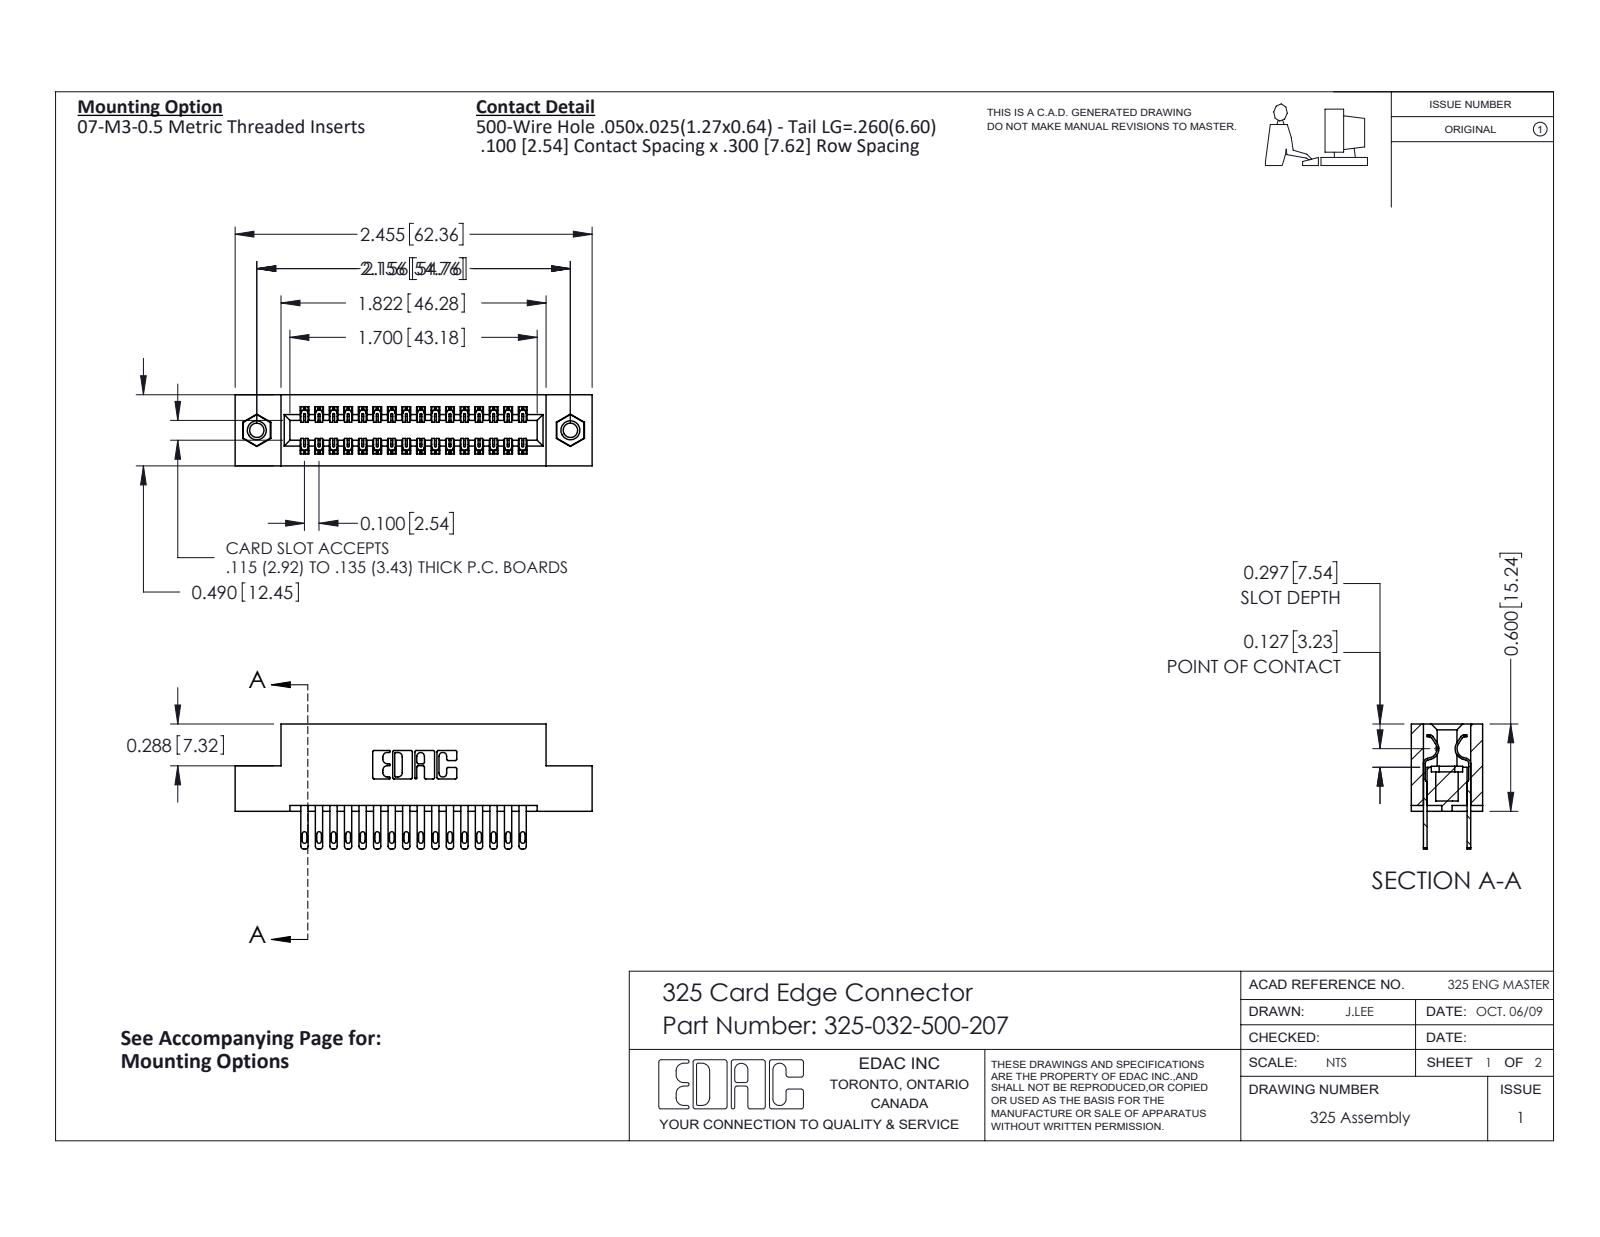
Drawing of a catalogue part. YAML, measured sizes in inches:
part_name: "345-250-001_345-250-005-103; 325-292-001_325-293-100; 325 Part_TI; 325-032-500-207"
step_written_by: "SolidWorks 2016 (CONFIG_CONTROL_DESIGN)"
units: inches
bodies: {solids: 35, faces: 1710, planar: 1062, cylindrical: 632, other: 16}
overall_size: [2.455, 0.86, 0.49]
volume: 0.482
surface_area: 14.43
round_holes:
  - {diameter: 0.098, count: 2}
  - {diameter: 0.125, count: 2}
  - {diameter: 0.16, count: 2}
round_bosses_or_shafts:
  - {diameter: 0.155, count: 2}
partial_cylinders:
  - {radius: 0.006, count: 48}
  - {radius: 0.016, count: 32}
  - {radius: 0.02, count: 32}
  - {radius: 0.01, count: 22}
  - {radius: 0.007, count: 6}
  - {radius: 0.031, count: 6}
  - {radius: 0.026, count: 3}
  - {radius: 0.014, count: 2}
face_to_face_distances: [0.083, 0.407, 0.3, 0.107, 0.383, 0.025, 0.49, 0.325, 0.04, 0.1]
hole_center_spacings: [2.156]
